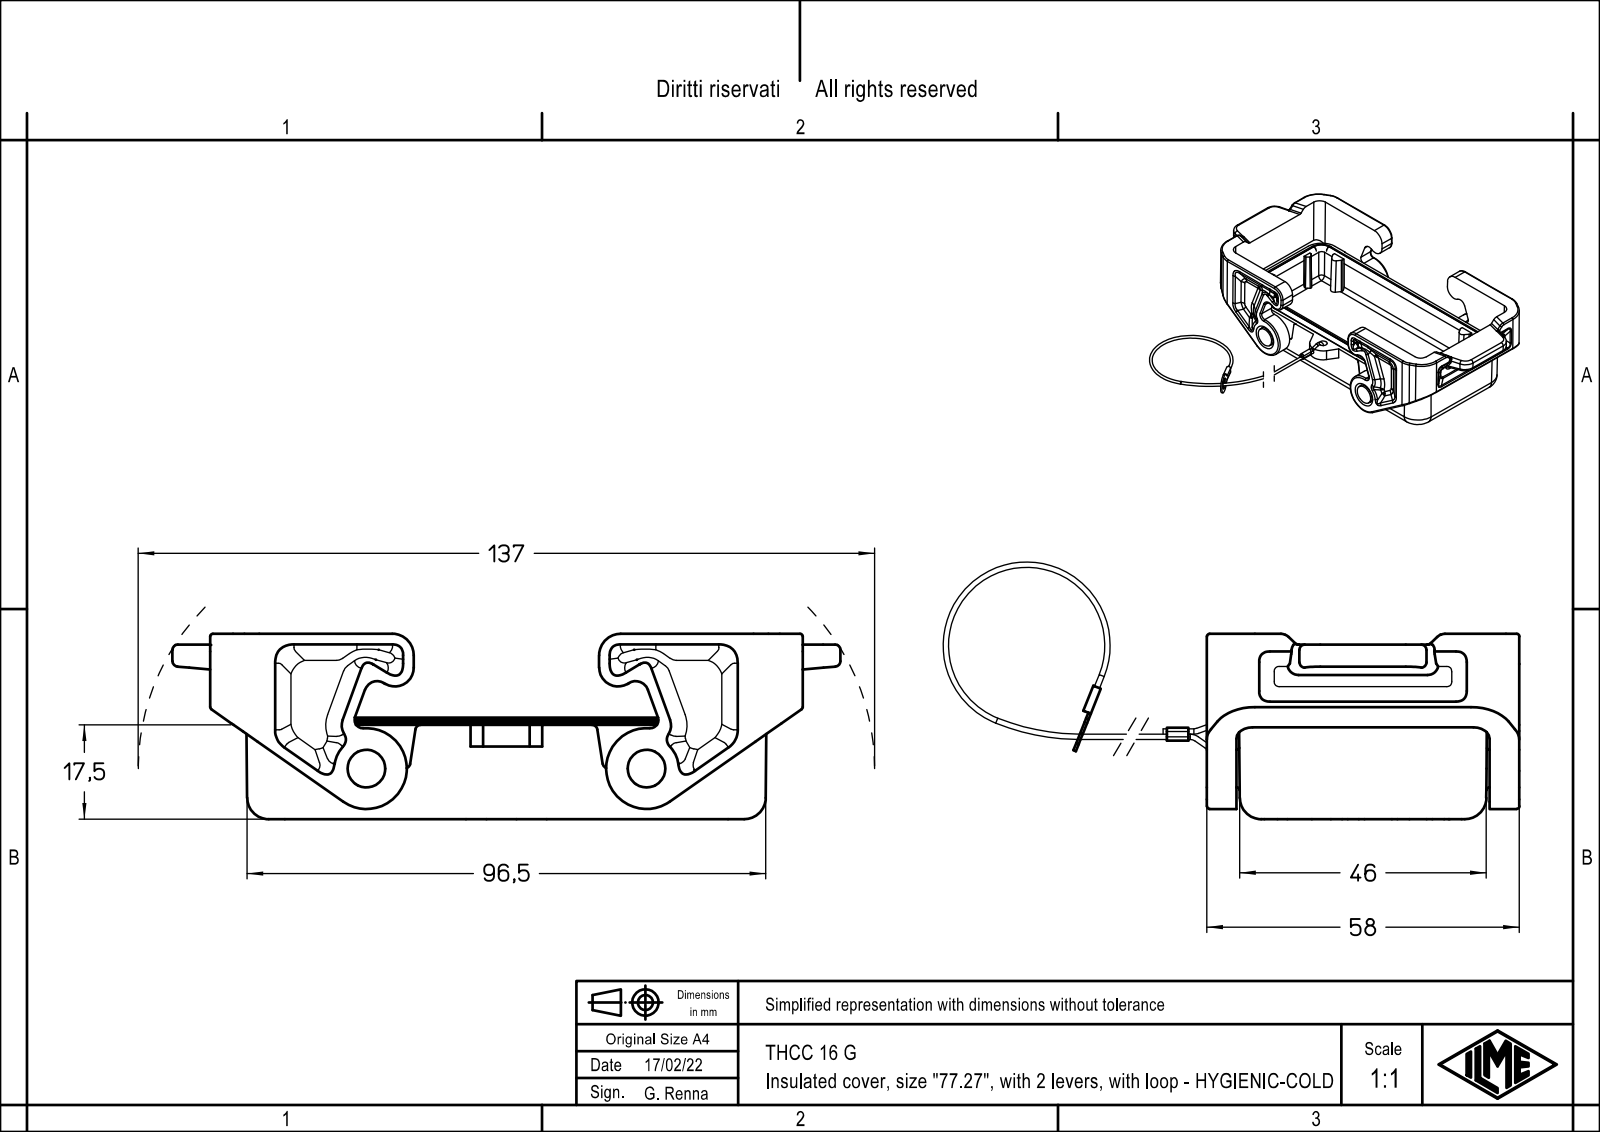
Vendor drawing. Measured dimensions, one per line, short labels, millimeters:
name: Coperchietto_16p_leve
written by: Creo Elements/Direct Modeling 20.1B 02-Apr-2019 (C) Parametric Technology GmbH (AUTOMOTIVE_DESIGN)
unit: mm
bodies: 1 solid, 604 faces (214 planar, 302 cylindrical, 88 other)
size: 227.87 × 124 × 34.55
volume: 66 119 mm³; area: 35 204 mm²
holes: 1× ⌀3, 1× ⌀4.2
bosses: 5× ⌀1, 3× ⌀7
rounds: 44× R0.15, 40× R1, 18× R1.5, 16× R1.3, 16× R3, 12× R0.5, 12× R2, 10× R4
face distances: 5.5, 52.5, 47, 34.4, 28.9, 12, 58, 17.5, 16.9, 100
